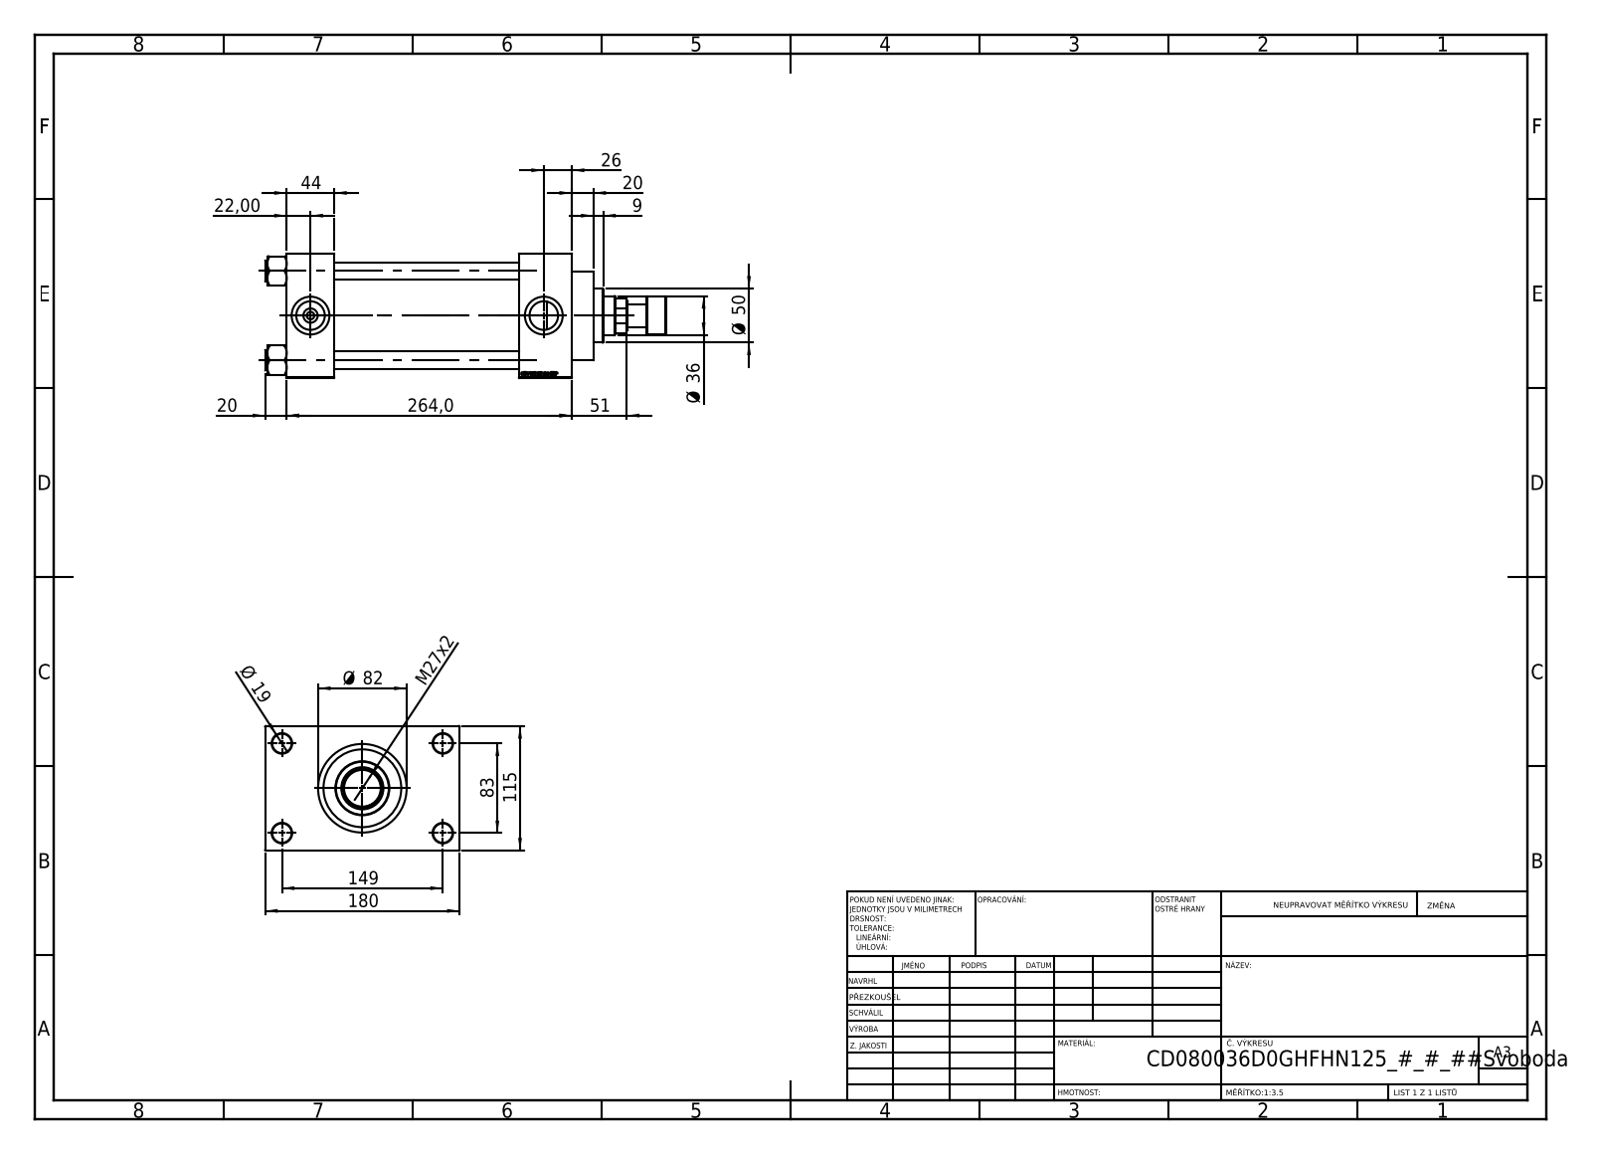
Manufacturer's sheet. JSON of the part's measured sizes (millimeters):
{"part_name": "V215CD_VCP_D; V215CR_ROD_END_F; V215CD_NUT_M5_D; V215CD_D_TYCINKA (+2 more)", "step_written_by": "SolidWorks 2019 (CONFIG_CONTROL_DESIGN)", "units": "millimeters", "bodies": {"solids": 12, "faces": 1165, "planar": 549, "cylindrical": 92, "other": 524}, "overall_size": [371, 180, 115], "volume_mm3": 2277000, "surface_area_mm2": 389906, "round_holes": [[16, 4], [18, 4], [7, 2], [26.44, 2], [35, 2], [25.5, 1], [36, 1], [39, 1], [61, 1], [72, 1], [80, 1]], "round_bosses_or_shafts": [[19, 4], [86, 1], [82, 1], [50, 1], [35, 1], [21, 1]], "face_to_face_distances": [115, 171, 49, 220, 44, 215, 264, 32.5, 147.5, 180], "hole_center_spacings": [33.15, 58.48, 82.7, 85.28, 89.24, 115.85, 142.43, 83]}
